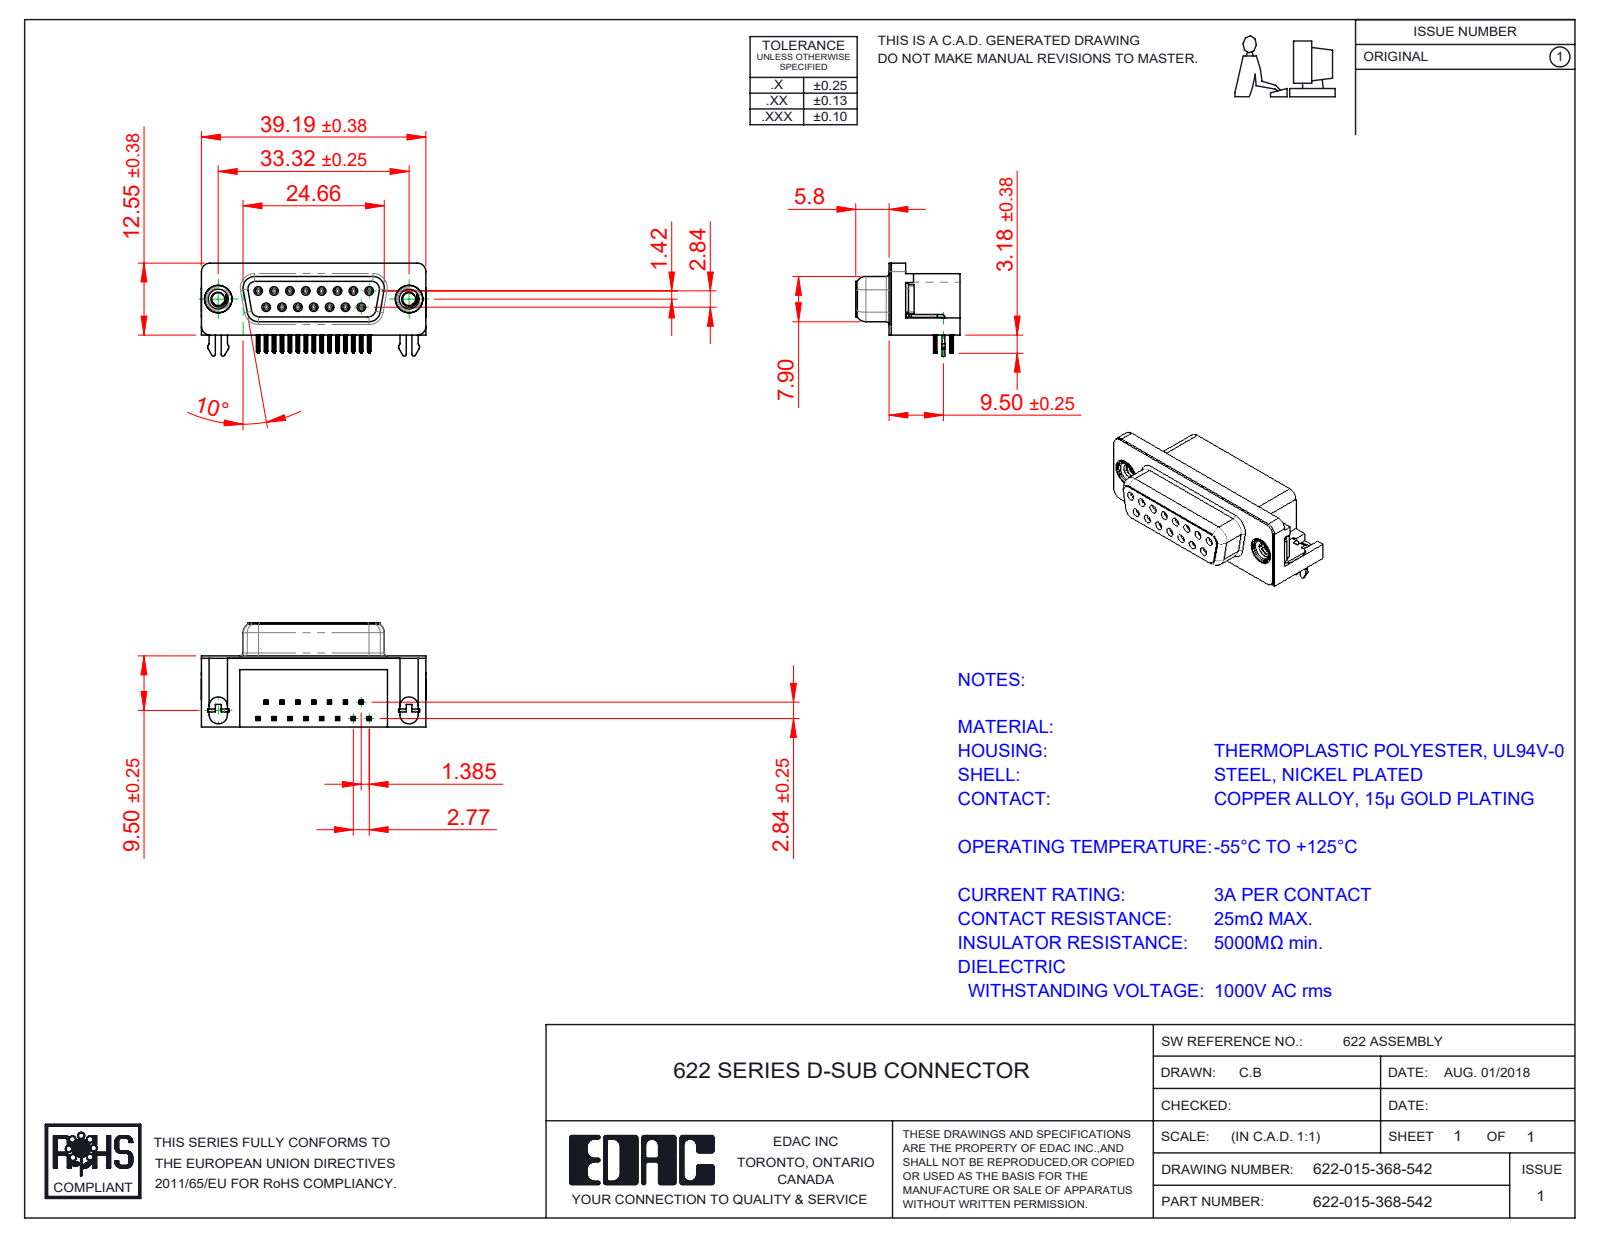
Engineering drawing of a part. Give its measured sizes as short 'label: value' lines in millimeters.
name: 622 Contact Top; 622-015-368-542; 622 Shell_15 Socket; 622 Housing_15 Socket (+3 more)
written by: SolidWorks 2016 (CONFIG_CONTROL_DESIGN)
unit: mm
bodies: 21 solids, 2547 faces (1116 planar, 611 cylindrical, 820 other)
size: 39.22 × 18.2 × 16.25
volume: 5 199 mm³; area: 6 791 mm²
holes: 15× ⌀0.8, 15× ⌀0.9, 2× ⌀2, 2× ⌀2.26, 2× ⌀4, 2× ⌀4.8, 2× ⌀5
bosses: 15× ⌀1.2, 2× ⌀4.9, 2× ⌀4.75, 2× ⌀3.9, 2× ⌀3
rounds: 120× R0.1, 60× R0.15, 30× R0.35, 18× R1, 15× R0.34, 12× R0.25, 8× R1.35, 8× R1.5
face distances: 0.4, 12, 6.2, 12.4, 10.35, 2.9, 6.65, 0.85, 0.35, 5.8
hole spacings: 3.16, 2.77, 5.54, 8.31, 11.08, 5.03, 5.04, 7.48
